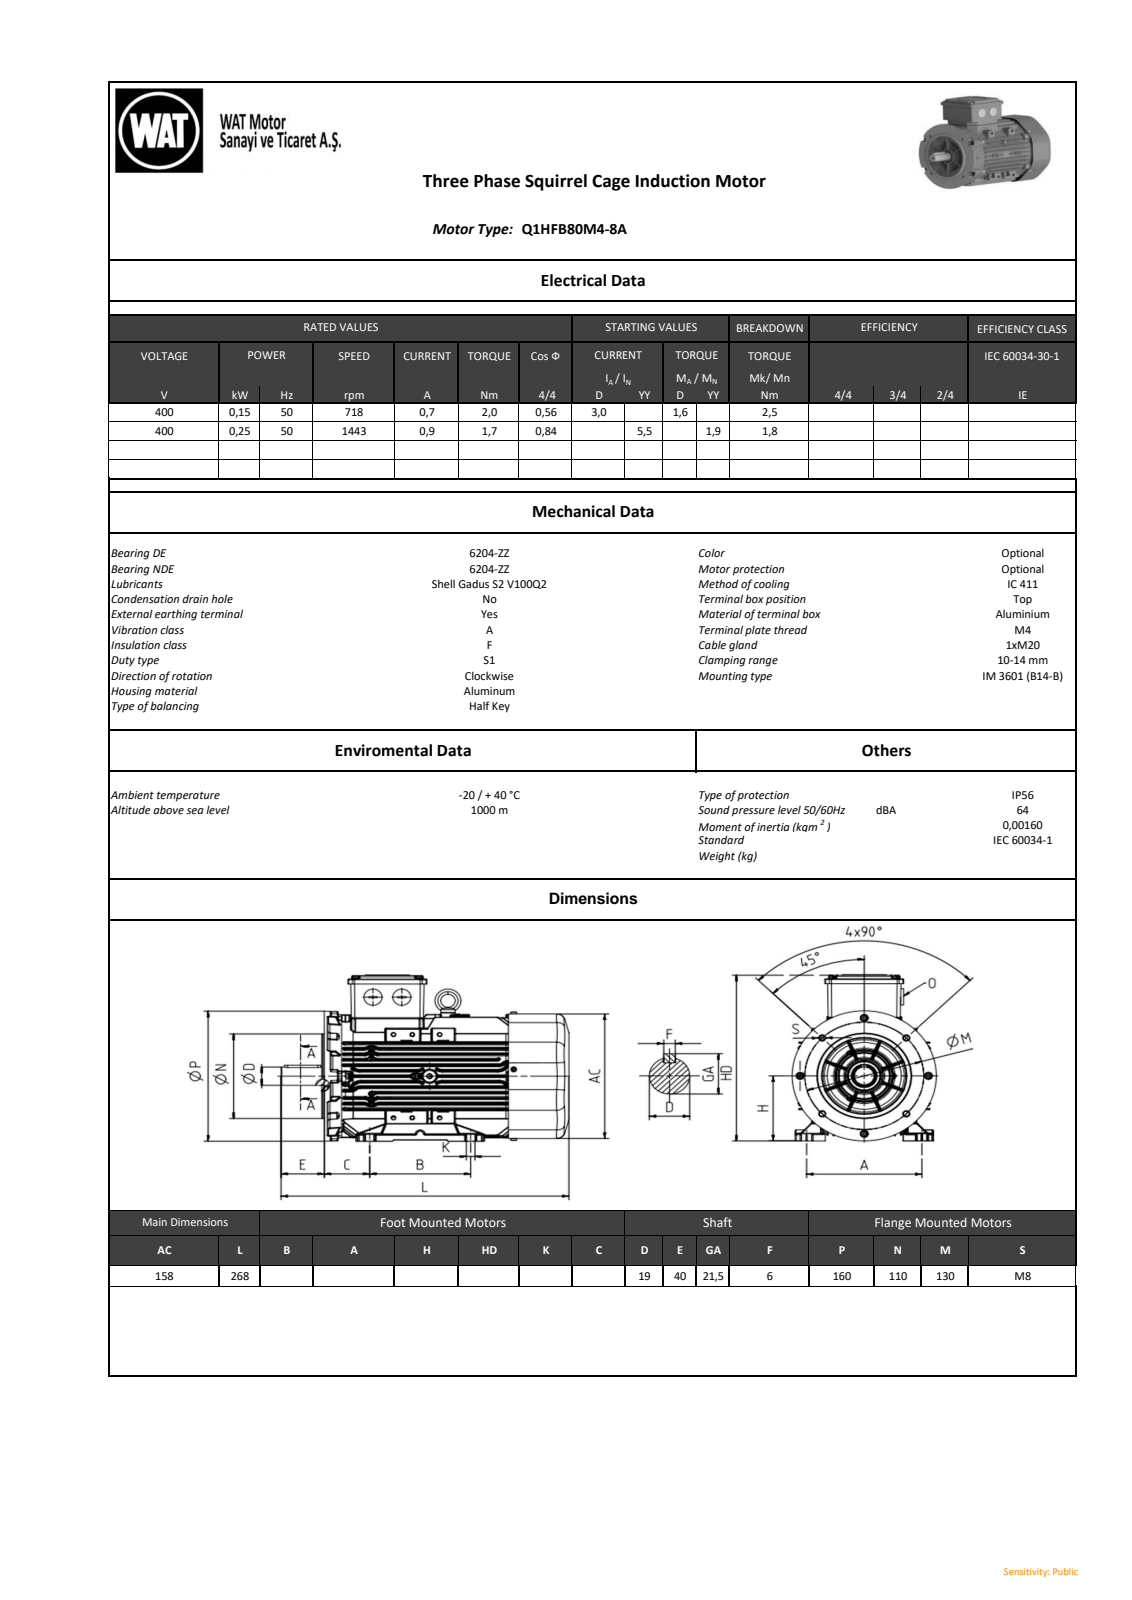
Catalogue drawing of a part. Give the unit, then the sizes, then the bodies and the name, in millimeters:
Units: millimetres
Overall size (bounding box): 268 × 215.5 × 160
Round holes (diameter × count): ⌀4.6 ×2, ⌀5 ×1, ⌀8 ×1, ⌀57 ×1
Round bosses / shafts (diameter × count): ⌀6 ×8, ⌀21.38 ×2, ⌀146.5 ×1, ⌀110 ×1, ⌀61 ×1, ⌀24.07 ×1, ⌀20.2 ×1, ⌀20 ×1
Partial cylindrical surfaces — rounded edges, fillets, slot ends (radius × count): R0.5 ×565, R1 ×530, R0.8 ×339, R2 ×89, R1.5 ×32, R0.5 ×20, R1.45 ×16, R5 ×14
Main face-to-face distances: 1, 157, 41.96, 156.98, 10.36, 86, 10.49, 52.32, 18, 20.84
Hole centre spacings: 70.94
Bodies: 0 solids, 5417 faces (1102 planar, 2149 cylindrical, 2166 other)
Part name (STEP PRODUCT): QH series_ 80_B14b_stp_objects
STEP written by: SIEMENS PLM Software NX2206.8101 (AUTOMOTIVE_DESIGN)
